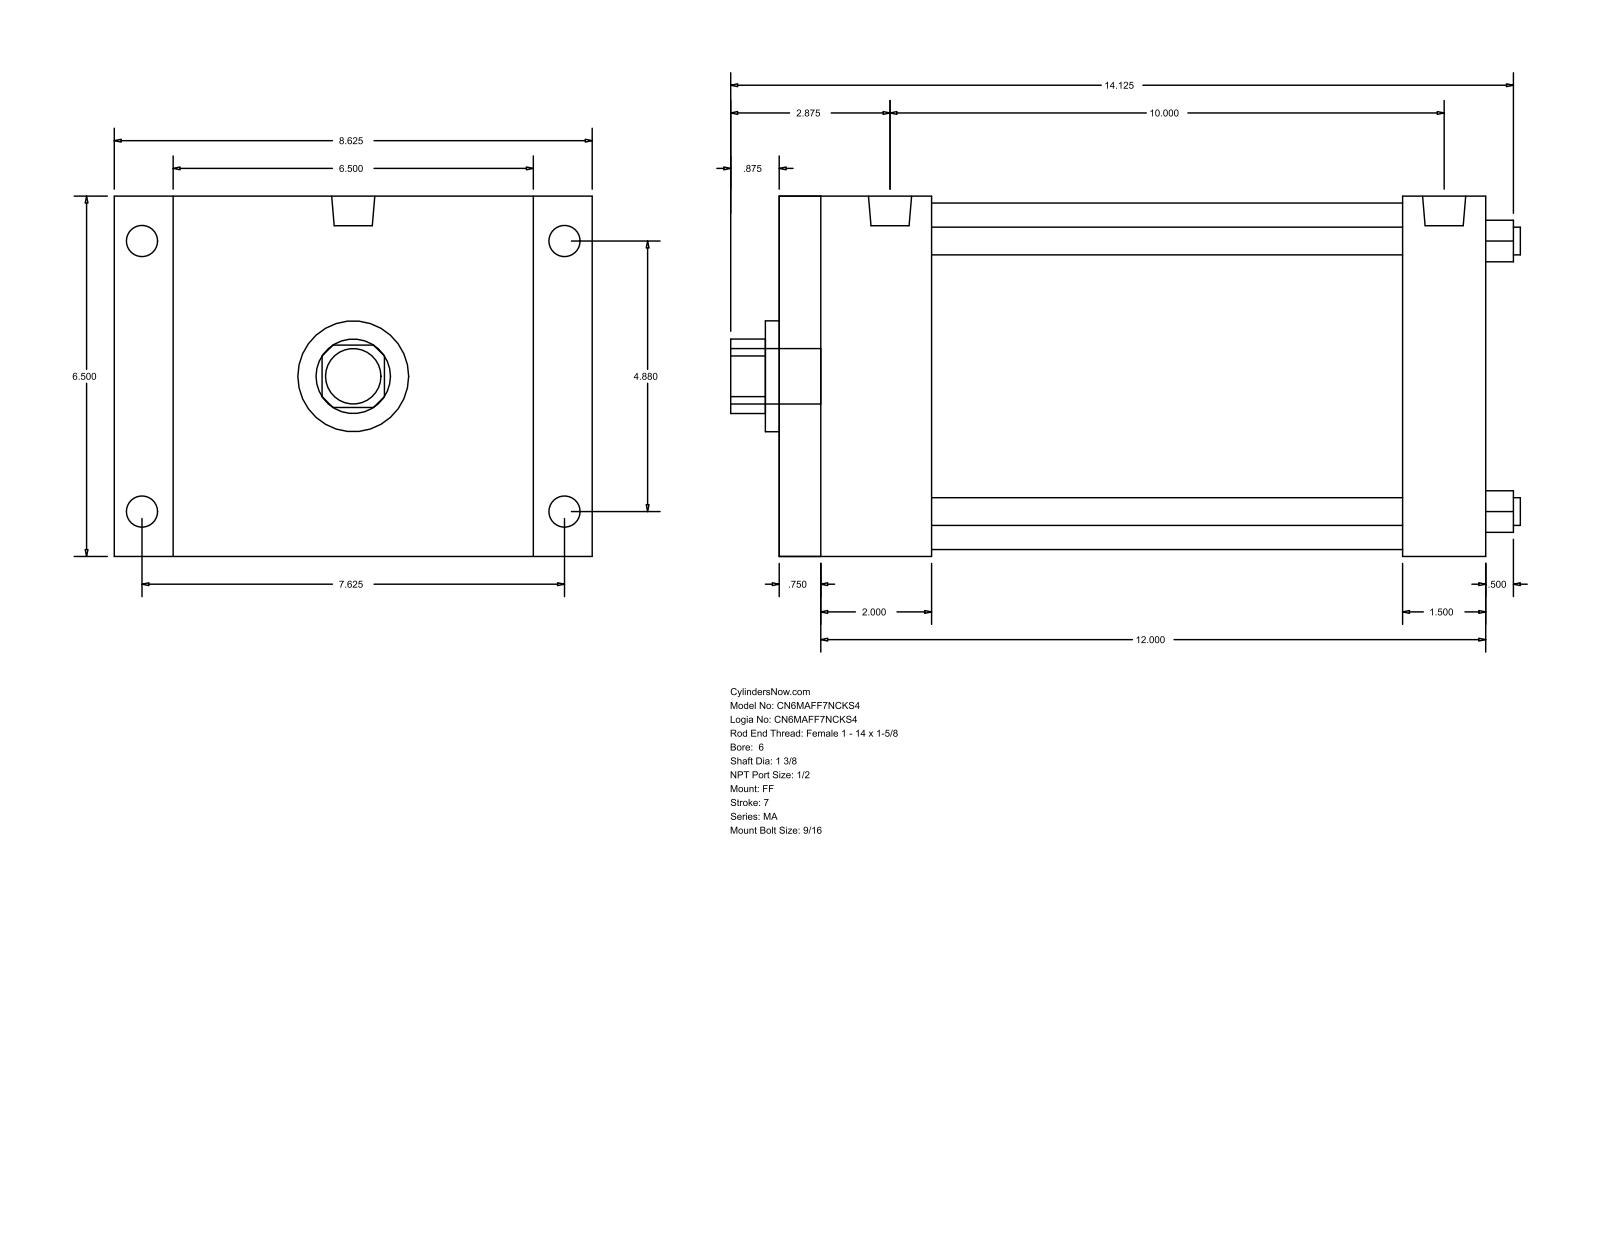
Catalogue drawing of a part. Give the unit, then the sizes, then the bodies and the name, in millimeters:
Units: millimetres
Overall size (bounding box): 361.95 × 219.07 × 165.1
Round holes (diameter × count): ⌀12.7 ×4, ⌀34.92 ×1, ⌀50.8 ×1, ⌀158.75 ×1
Round bosses / shafts (diameter × count): ⌀17.46 ×4, ⌀14.29 ×4, ⌀19.77 ×2, ⌀25.4 ×1
Partial cylindrical surfaces — rounded edges, fillets, slot ends (radius × count): R17.06 ×1
Main face-to-face distances: 165.1, 323.84, 219.08, 15.87, 307.97, 66.67, 50.8, 257.17, 285.75, 269.88
Hole centre spacings: 87.65, 123.96, 175.31
Bodies: 0 solids, 92 faces (64 planar, 28 cylindrical, 0 other)
Part name (STEP PRODUCT): MA_FF__0600_1.375
STEP written by: GSSL Pune (CONFIG_CONTROL_DESIGN)
